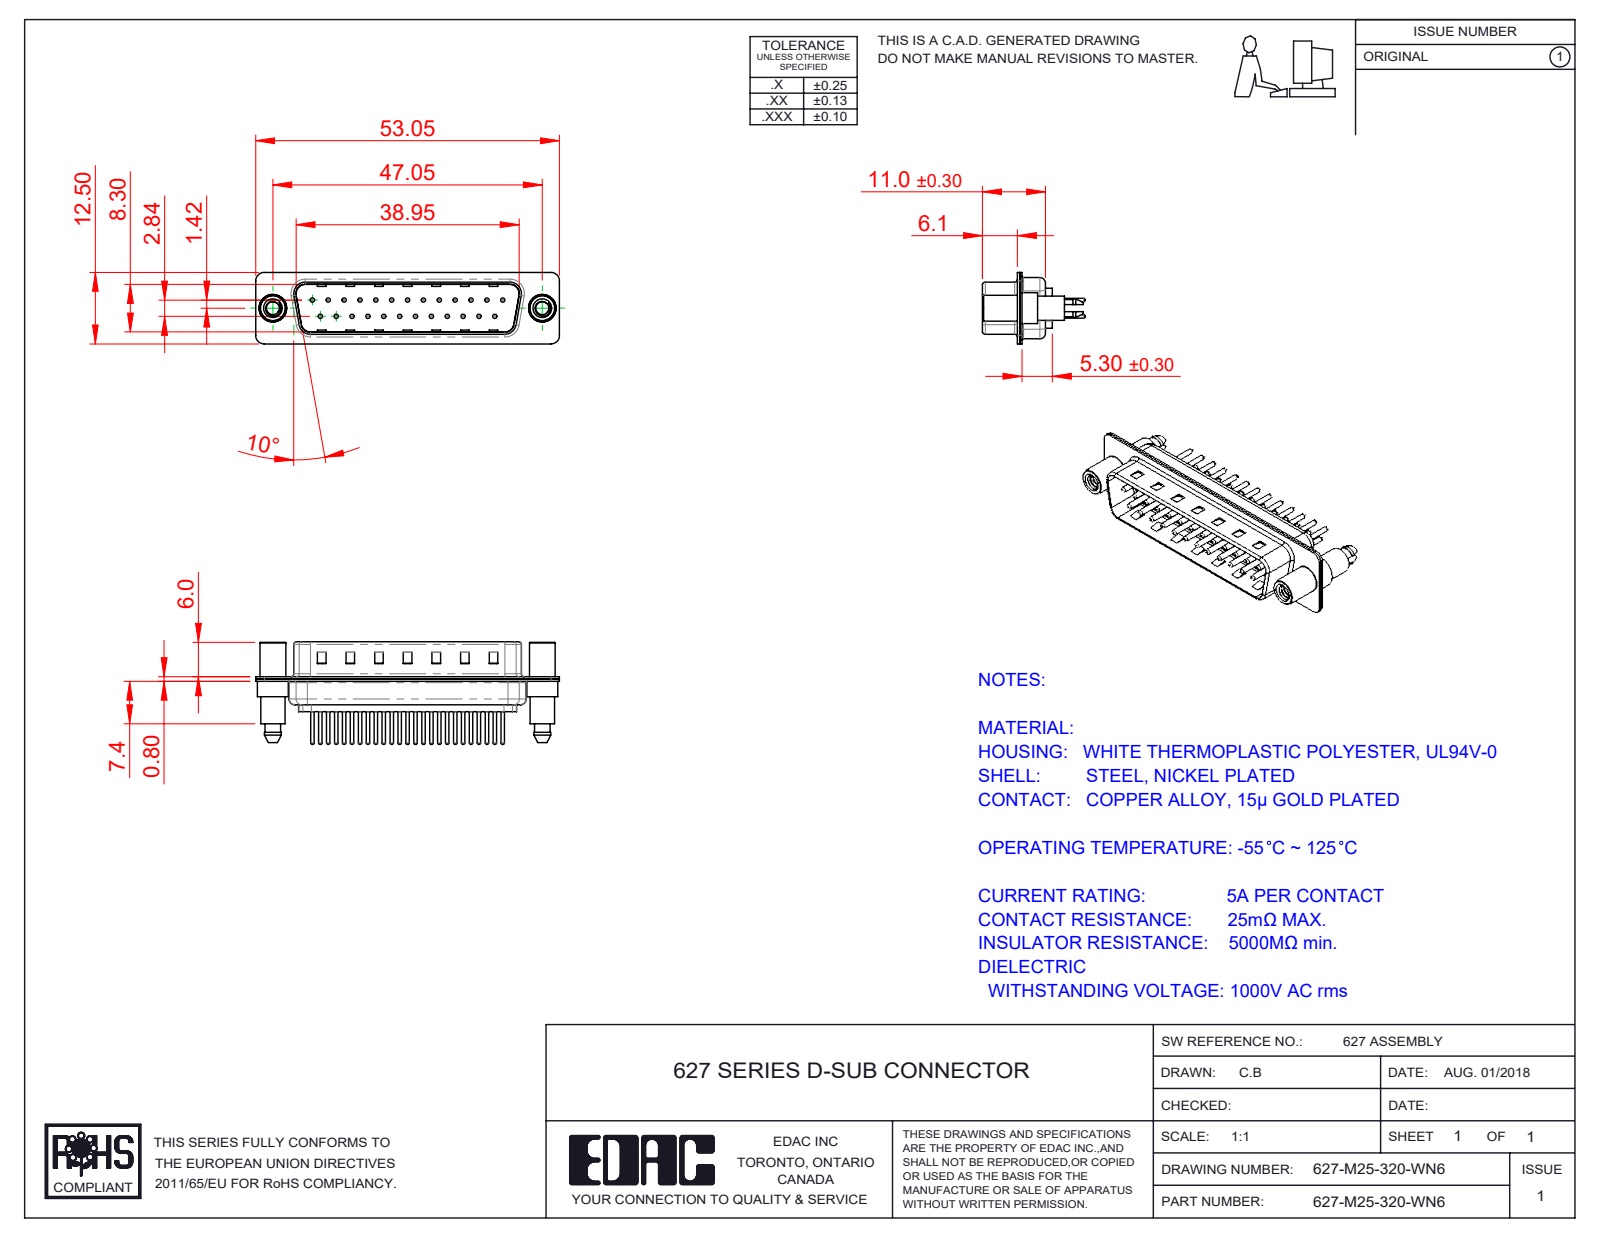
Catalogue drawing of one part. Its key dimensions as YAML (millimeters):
part_name: "627M Shell Rear_25 Contacts; 627M Shell Front_25 Contacts; 627M 4-40 Threaded Standoff and Boardlock; 627-M25-320-WN6 (+3 more)"
step_written_by: "SolidWorks 2020 (CONFIG_CONTROL_DESIGN)"
units: millimeters
bodies: {solids: 30, faces: 1353, planar: 364, cylindrical: 515, other: 474}
overall_size: [53.05, 17.9, 12.5]
volume: 3058
surface_area: 7311
round_holes:
  - {diameter: 0.75, count: 25}
  - {diameter: 1.6, count: 25}
  - {diameter: 2, count: 25}
  - {diameter: 2.26, count: 2}
  - {diameter: 4, count: 2}
  - {diameter: 4.8, count: 2}
round_bosses_or_shafts:
  - {diameter: 1.5, count: 25}
  - {diameter: 0.6, count: 25}
  - {diameter: 5.4, count: 2}
  - {diameter: 4.9, count: 2}
  - {diameter: 4.5, count: 2}
  - {diameter: 4.25, count: 2}
partial_cylinders:
  - {radius: 1.5, count: 18}
  - {radius: 2, count: 12}
  - {radius: 1.6, count: 10}
  - {radius: 0.5, count: 8}
  - {radius: 0.25, count: 4}
  - {radius: 0.6, count: 4}
  - {radius: 0.65, count: 4}
  - {radius: 0.9, count: 4}
face_to_face_distances: [0.4, 0.8, 9.5, 9.1, 8.7, 9.9, 1.2, 5.7, 6.1, 0.75]
hole_center_spacings: [3.16, 2.77, 5.54, 8.31, 11.08, 13.85, 16.62, 5.03]
